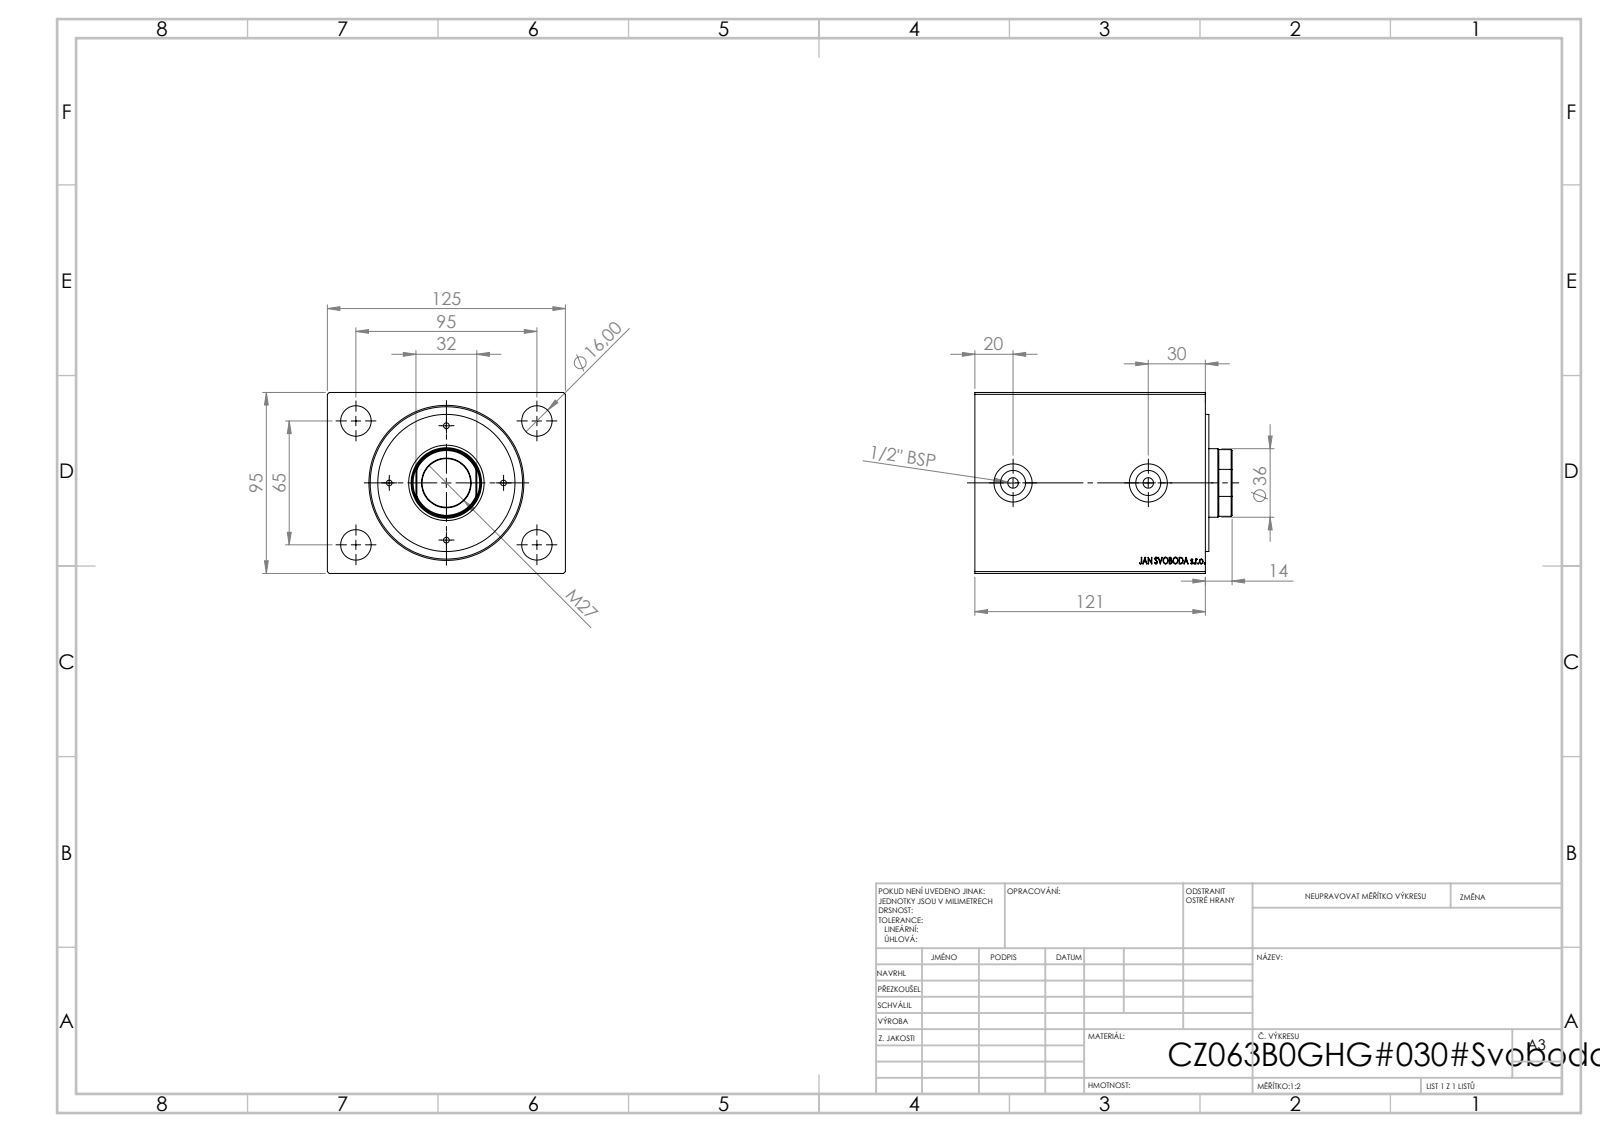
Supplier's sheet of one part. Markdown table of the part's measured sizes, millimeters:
| quantity | value |
| --- | --- |
| part name | V500CZ; V500CZ_B_VC |
| STEP written by | SolidWorks 2019 (CONFIG_CONTROL_DESIGN) |
| units | millimeters |
| bodies | 3 solids, 874 faces (400 planar, 58 cylindrical, 416 other) |
| overall size | 135 × 125 × 95 |
| volume | 1 315 000 mm³ |
| surface area | 149 170 mm² |
| round holes (diameter × count) | 3 × 4, 16 × 4, 5.5 × 2, 13.16 × 2, 20 × 2, 25.5 × 1, 36 × 1, 37 × 1, 63 × 1, 80 × 1 |
| round bosses / shafts (diameter × count) | 72 × 1 |
| partial cylindrical surfaces (radius × count) | 17.5 × 1 |
| main face-to-face distances | 95, 125, 121, 100.2, 20.8, 14, 1.8, 12.2, 88, 108.8 |
| hole center spacings | 30, 36.91, 42.43, 47.57, 57.55, 78.5, 84.04, 60 |
